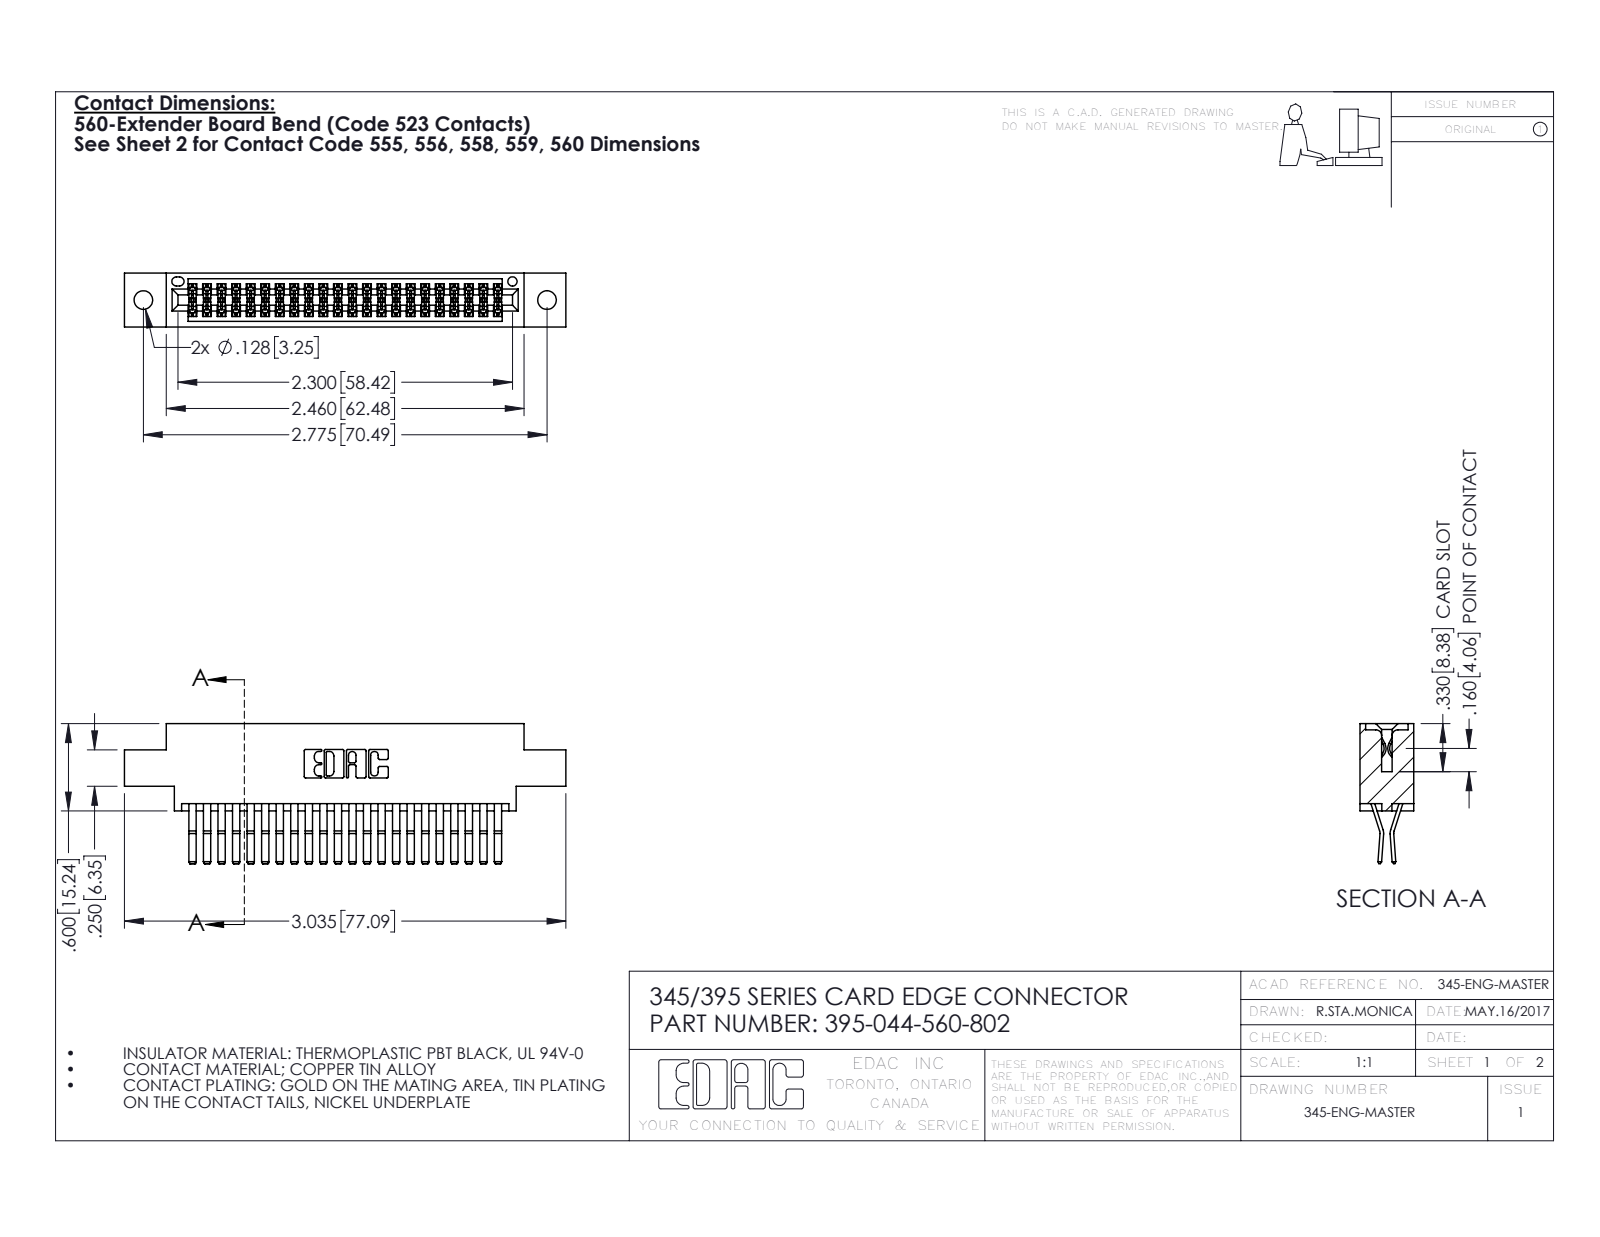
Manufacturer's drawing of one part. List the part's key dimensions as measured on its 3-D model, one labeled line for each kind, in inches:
Part name (STEP PRODUCT): 345-292-001_560 Tail; 345 Part_0.170 Offset - 0.128 Dia; 395-044-560-802
STEP written by: SolidWorks 2016 (CONFIG_CONTROL_DESIGN)
Units: inches
Bodies: 45 solids, 2418 faces (1536 planar, 882 cylindrical, 0 other)
Overall size (bounding box): 3.035 × 0.962 × 0.37
Volume: 0.454 in³ · Surface area: 17.4 in²
Round holes (diameter × count): ⌀0.128 ×2, ⌀0.064 ×1
Partial cylindrical surfaces — rounded edges, fillets, slot ends (radius × count): R0.006 ×67, R0.01 ×22, R0.007 ×6, R0.031 ×6, R0.026 ×3, R0.01 ×2, R0.014 ×2, R0.019 ×2
Main face-to-face distances: 0.025, 0.298, 0.072, 0.37, 0.2, 0.098, 0.272, 0.225, 0.175, 0.15
Hole centre spacings: 0.27, 2.541, 2.775
